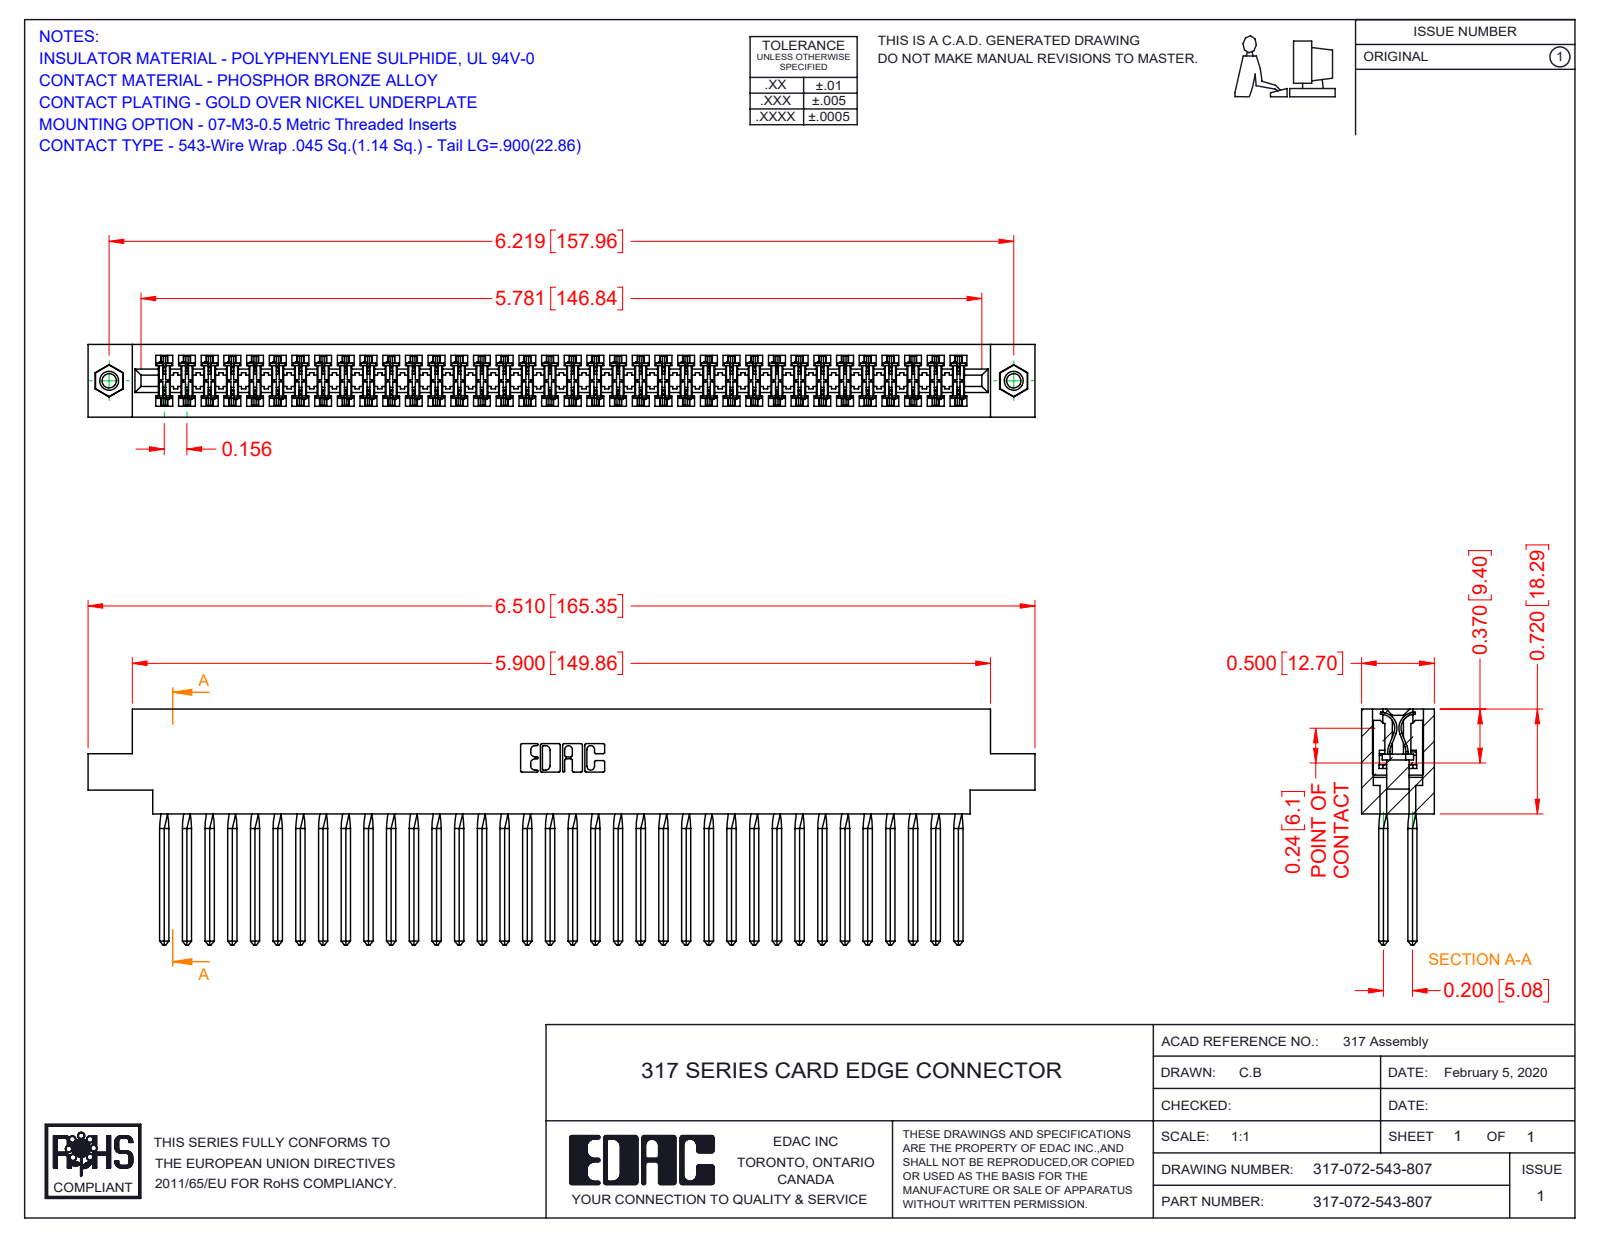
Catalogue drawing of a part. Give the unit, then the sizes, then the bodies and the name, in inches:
Units: inches
Overall size (bounding box): 6.51 × 1.62 × 0.5
Round holes (diameter × count): ⌀0.098 ×2, ⌀0.125 ×2, ⌀0.156 ×2
Round bosses / shafts (diameter × count): ⌀0.155 ×2
Partial cylindrical surfaces — rounded edges, fillets, slot ends (radius × count): R0.015 ×144, R0.01 ×22, R0.007 ×6, R0.031 ×6, R0.026 ×3, R0.095 ×2, R0.1 ×2, R0.11 ×2
Main face-to-face distances: 0.5, 0.075, 0.425, 0.35, 0.11, 0.195, 0.094, 0.2, 0.115, 0.131
Hole centre spacings: 6.219
Volume: 1.702 in³ · Surface area: 65.28 in²
Bodies: 75 solids, 6570 faces (5346 planar, 920 cylindrical, 304 other)
Part name (STEP PRODUCT): 317 Part_.156 Dia - TI; 317-290-001_543; 317-072-543-807; 345-250-001_345-250-005-103
STEP written by: SolidWorks 2016 (CONFIG_CONTROL_DESIGN)
